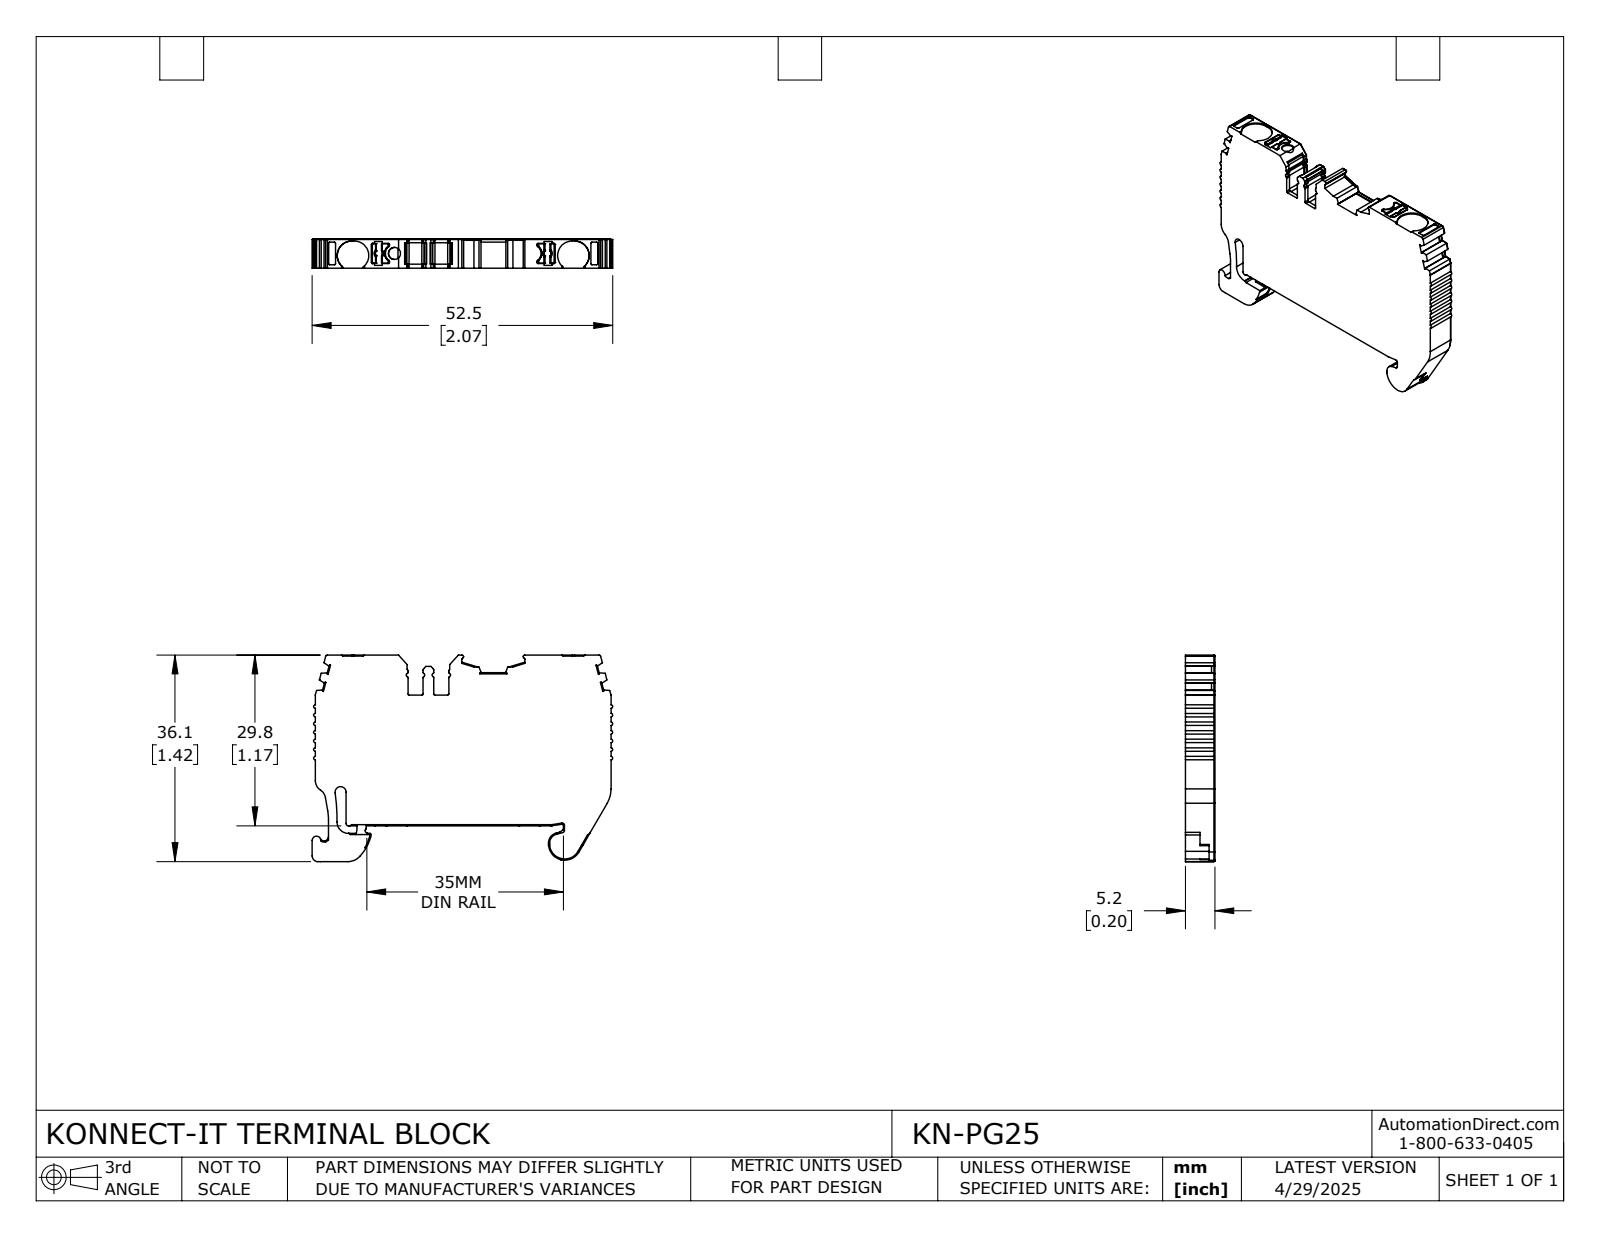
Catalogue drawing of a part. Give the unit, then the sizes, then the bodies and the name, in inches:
Units: inches
Overall size (bounding box): 2.066 × 1.42 × 0.203
Round holes (diameter × count): ⌀0.083 ×1
Partial cylindrical surfaces — rounded edges, fillets, slot ends (radius × count): R0.008 ×53, R0.012 ×42, R0.016 ×18, R0.004 ×17, R0.02 ×16, R0.006 ×8, R0.039 ×6, R0.1 ×4
Main face-to-face distances: 0.203, 1.166, 1.158, 1.174, 2.033, 0.177, 0.197, 0.211, 1.821, 0.246
Volume: 0.466 in³ · Surface area: 6.702 in²
Bodies: 1 solid, 634 faces (336 planar, 261 cylindrical, 37 other)
Part name (STEP PRODUCT): KN-PG25
STEP written by: SolidWorks 2024 (CONFIG_CONTROL_DESIGN)
